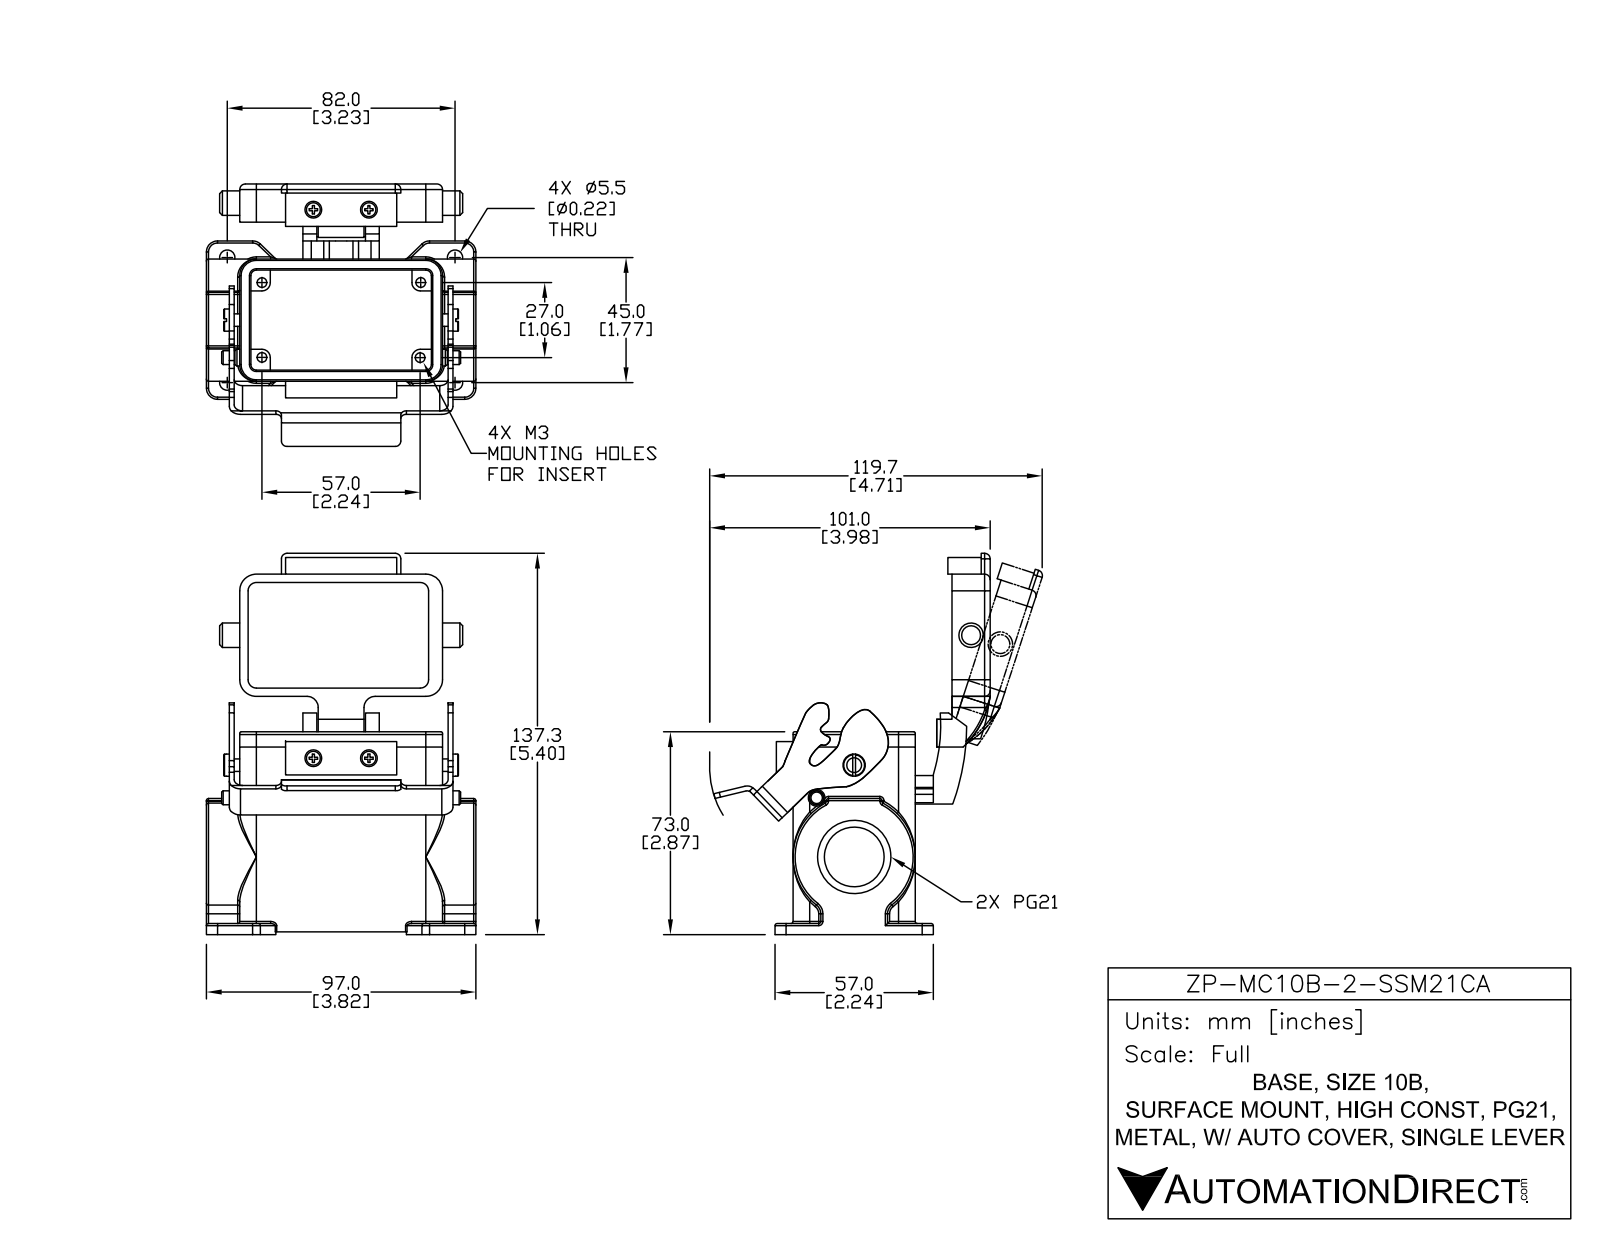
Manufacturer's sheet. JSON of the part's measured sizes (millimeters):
{"part_name": "ZP-MC10B-2-SSM21CA", "step_written_by": "SolidWorks 2014 (AUTOMOTIVE_DESIGN)", "units": "millimeters", "bodies": {"solids": 11, "faces": 610, "planar": 236, "cylindrical": 210, "other": 164}, "overall_size": [137.75, 97, 94.45], "volume_mm3": 146500, "surface_area_mm2": 75923, "round_holes": [[3, 4], [5.5, 4], [4.5, 1], [5.32, 1], [20.5, 1], [26.4, 1]], "round_bosses_or_shafts": [[5, 5], [8, 2], [8.8, 1], [6, 1]], "partial_cylinders_radius": [[0.5, 49], [2, 23], [4, 14], [3, 12], [6, 8], [21.95, 2], [3.75, 1], [4.25, 1]], "face_to_face_distances": [4, 40, 44, 1.75, 5, 12, 1, 36, 6, 69], "hole_center_spacings": [15.4, 38.11, 70.08, 78.27, 27, 45, 57, 63.07]}
